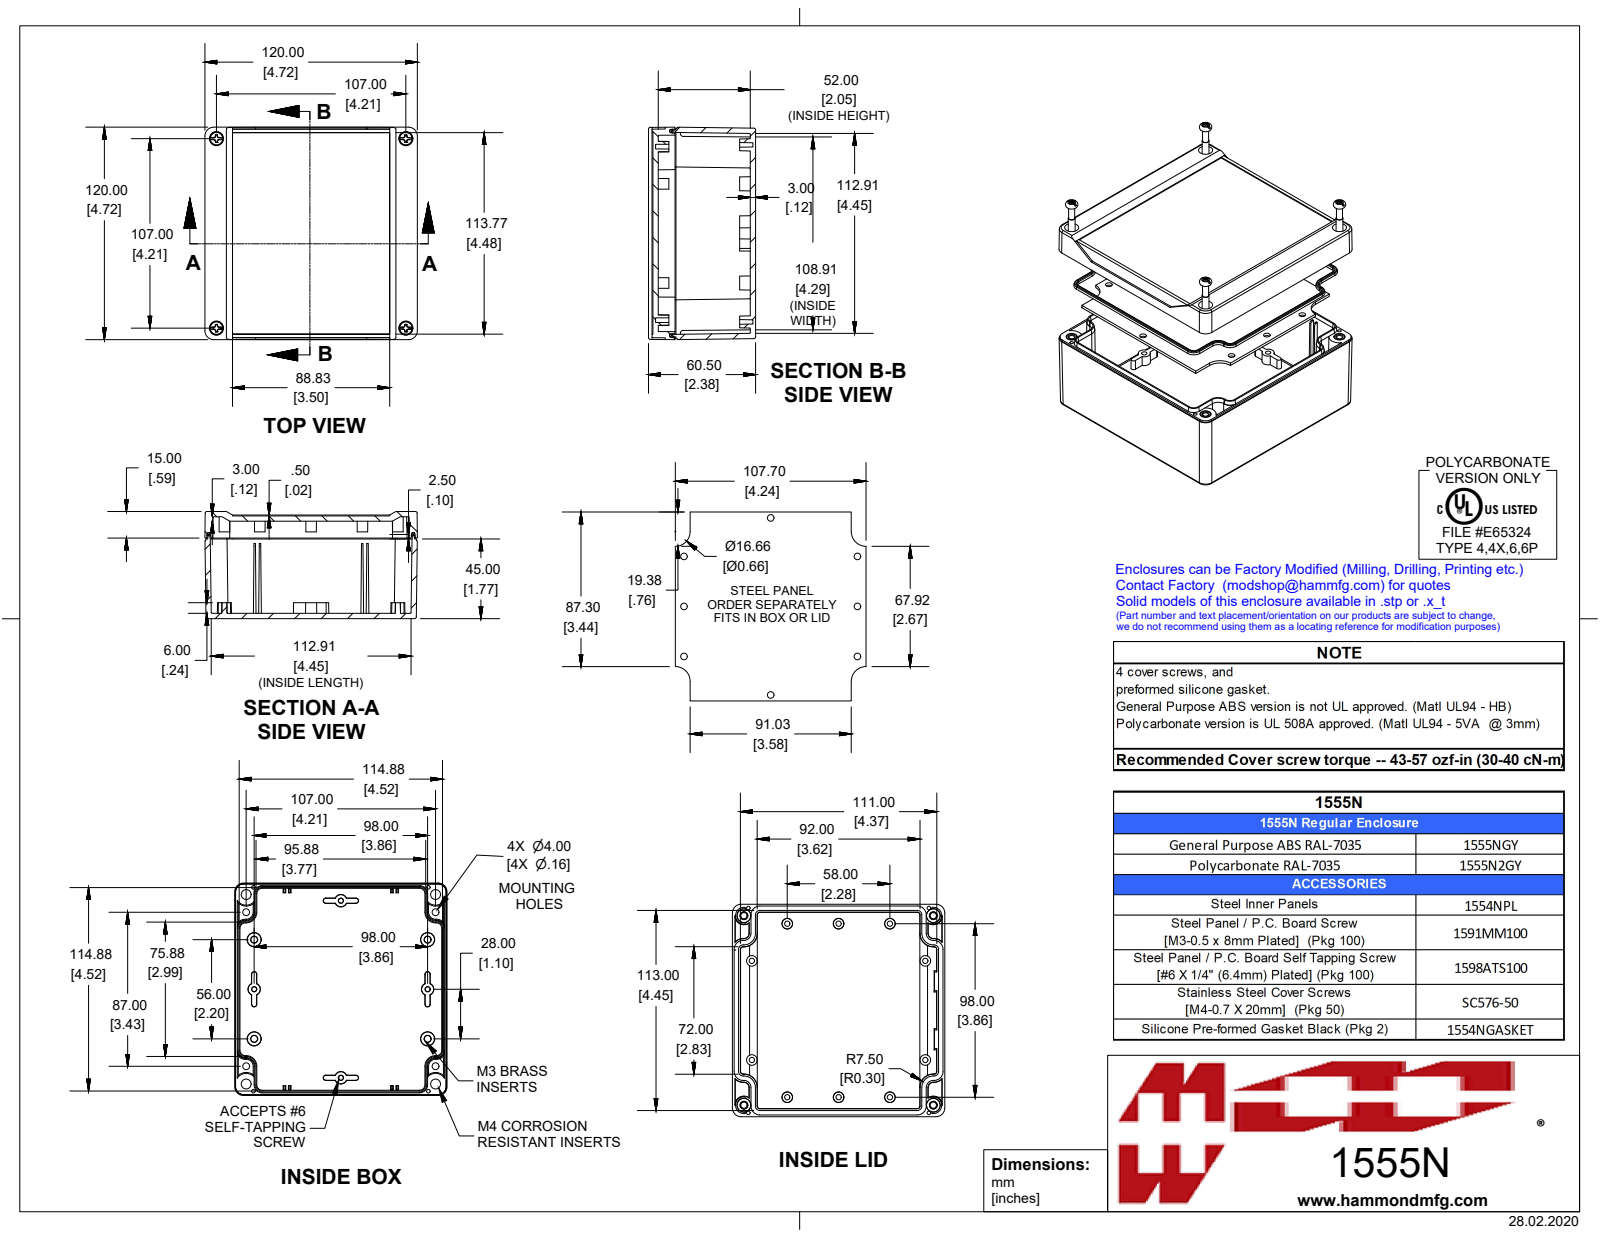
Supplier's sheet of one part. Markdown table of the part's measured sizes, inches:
| quantity | value |
| --- | --- |
| part name | 1555N2GY |
| STEP written by | SolidWorks 2019 (AUTOMOTIVE_DESIGN) |
| units | inches |
| bodies | 16 solids, 1420 faces (435 planar, 351 cylindrical, 634 other) |
| overall size | 4.724 × 4.724 × 2.382 |
| volume | 12.36 in³ |
| surface area | 247 in² |
| round holes (diameter × count) | 0.118 × 10, 0.079 × 8, 0.097 × 4, 0.11 × 4, 0.128 × 4, 0.138 × 4, 0.147 × 4 |
| round bosses / shafts (diameter × count) | 0.25 × 4, 0.236 × 4, 0.218 × 4, 0.21 × 4, 0.19 × 4, 0.154 × 4, 0.153 × 4, 0.15 × 4 |
| partial cylindrical surfaces (radius × count) | 0.02 × 40, 0.039 × 8, 0.197 × 8, 0.154 × 4, 0.187 × 4, 0.328 × 4, 0.059 × 2 |
| main face-to-face distances | 0.118, 2.165, 0.354, 0.236, 0.419, 0.3, 0.064, 1.929, 1.811, 2.283 |
| hole center spacings | 3.858, 1.142, 2.111, 2.114, 3.626, 4.552, 4.661, 0.197 |
